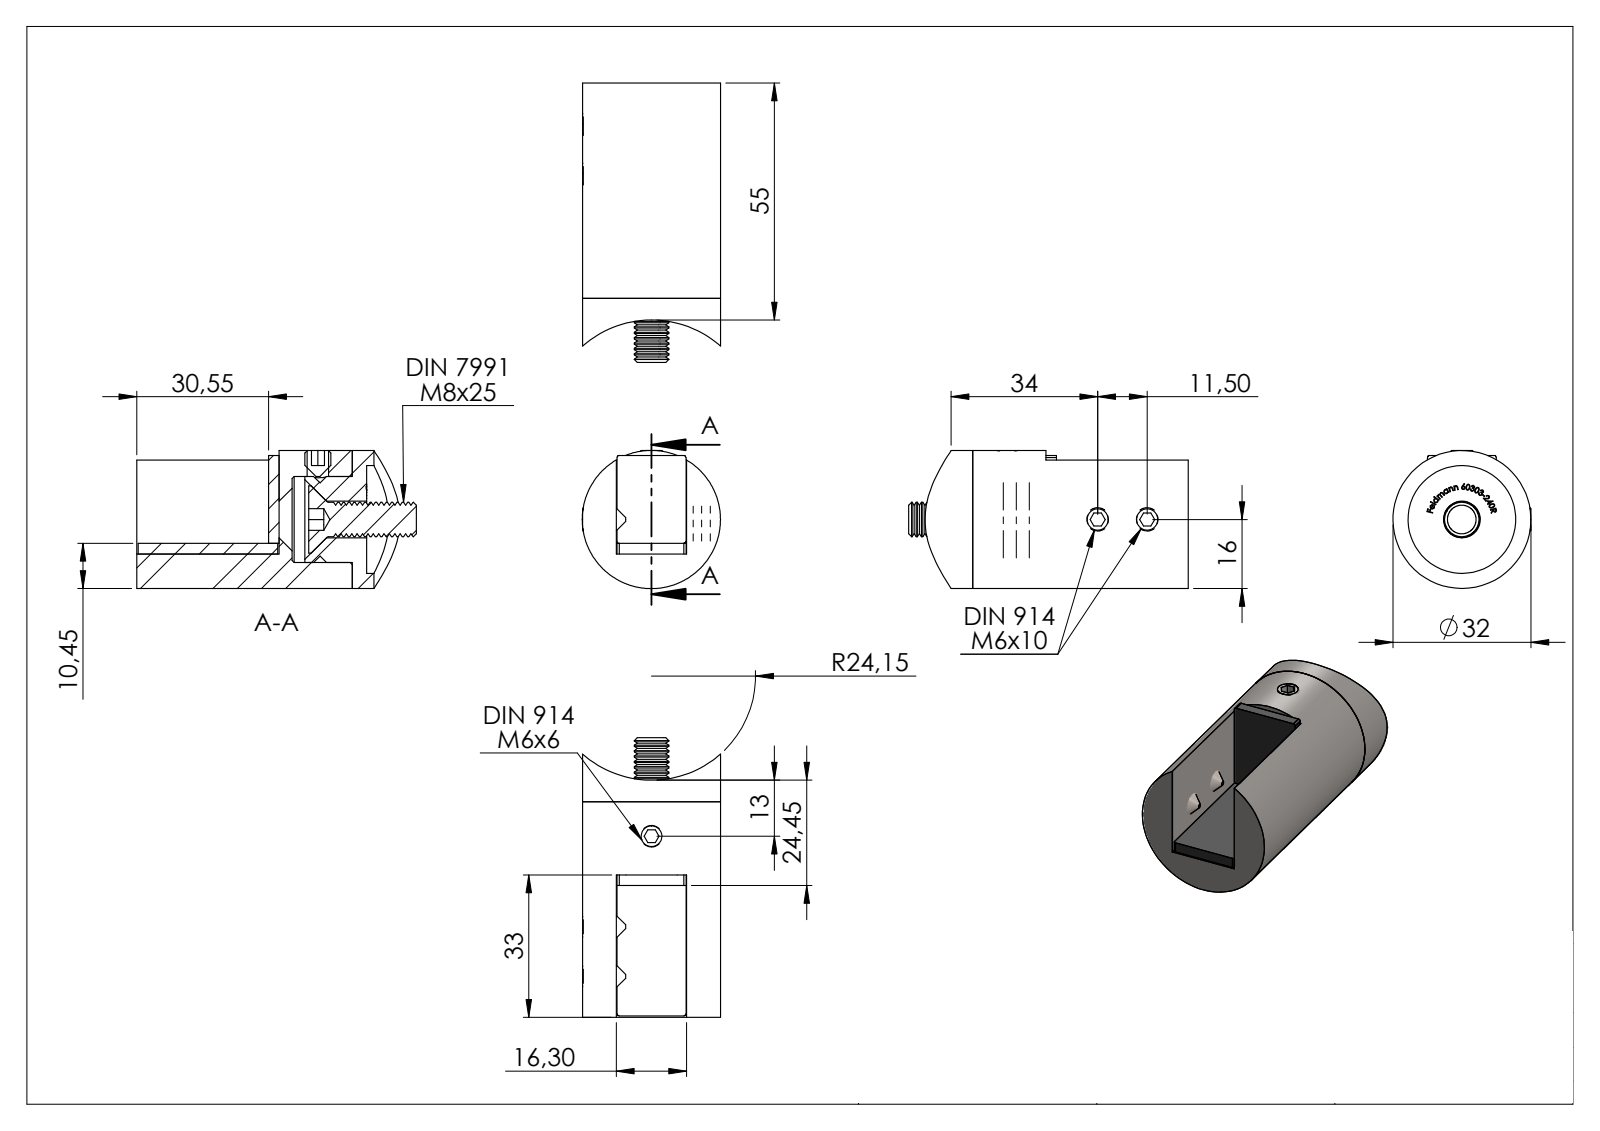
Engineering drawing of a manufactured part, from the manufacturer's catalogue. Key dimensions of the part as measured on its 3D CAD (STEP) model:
Part name (STEP PRODUCT): 60303-240R; 6030X-240X Teil4; 6030X-240X Teil1_6030X-240R Teil1; socket countersunk head screw_din_DIN 7991 - M8 x 25 --- 25S (+8 more)
STEP written by: SolidWorks 2018 (CONFIG_CONTROL_DESIGN)
Units: millimetres
Bodies: 8 solids, 445 faces (187 planar, 53 cylindrical, 205 other)
Overall size (bounding box): 70 × 64.85 × 32
Volume: 32 395 mm³ · Surface area: 16 864 mm²
Round holes (diameter × count): ⌀5 ×3, ⌀8.5 ×1, ⌀25 ×1
Round bosses / shafts (diameter × count): ⌀6 ×3, ⌀32 ×1, ⌀20 ×1, ⌀15.57 ×1, ⌀8 ×1
Partial cylindrical surfaces — rounded edges, fillets, slot ends (radius × count): R0.5 ×8, R24.15 ×1
Main face-to-face distances: 2.45, 16.3, 17, 3.3, 20.3, 53.3, 50, 33, 22.75, 19.45
Hole centre spacings: 11.5
